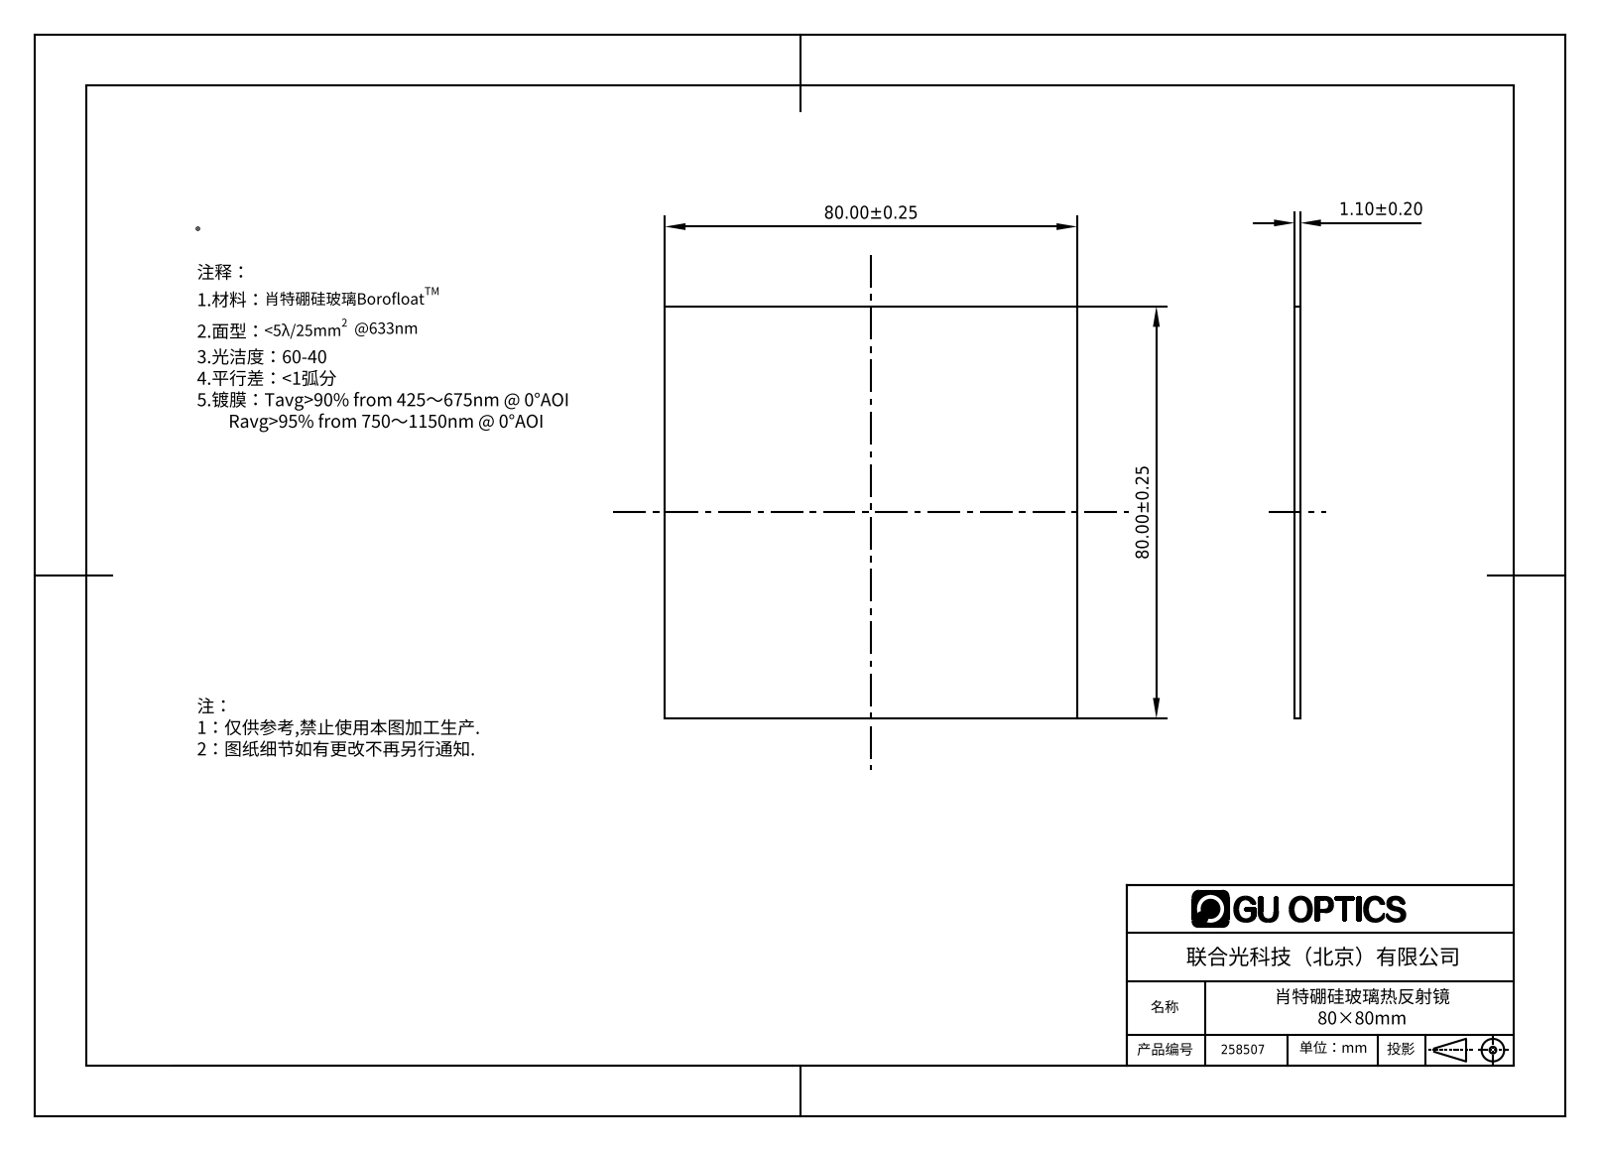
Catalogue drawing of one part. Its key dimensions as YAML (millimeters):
part_name: "258507"
step_written_by: "SolidWorks 2016 (AUTOMOTIVE_DESIGN)"
units: millimeters
bodies: {solids: 1, faces: 6, planar: 6, cylindrical: 0, other: 0}
overall_size: [80, 80, 1.1]
volume: 7040
surface_area: 13152
face_to_face_distances: [1.1, 80]
